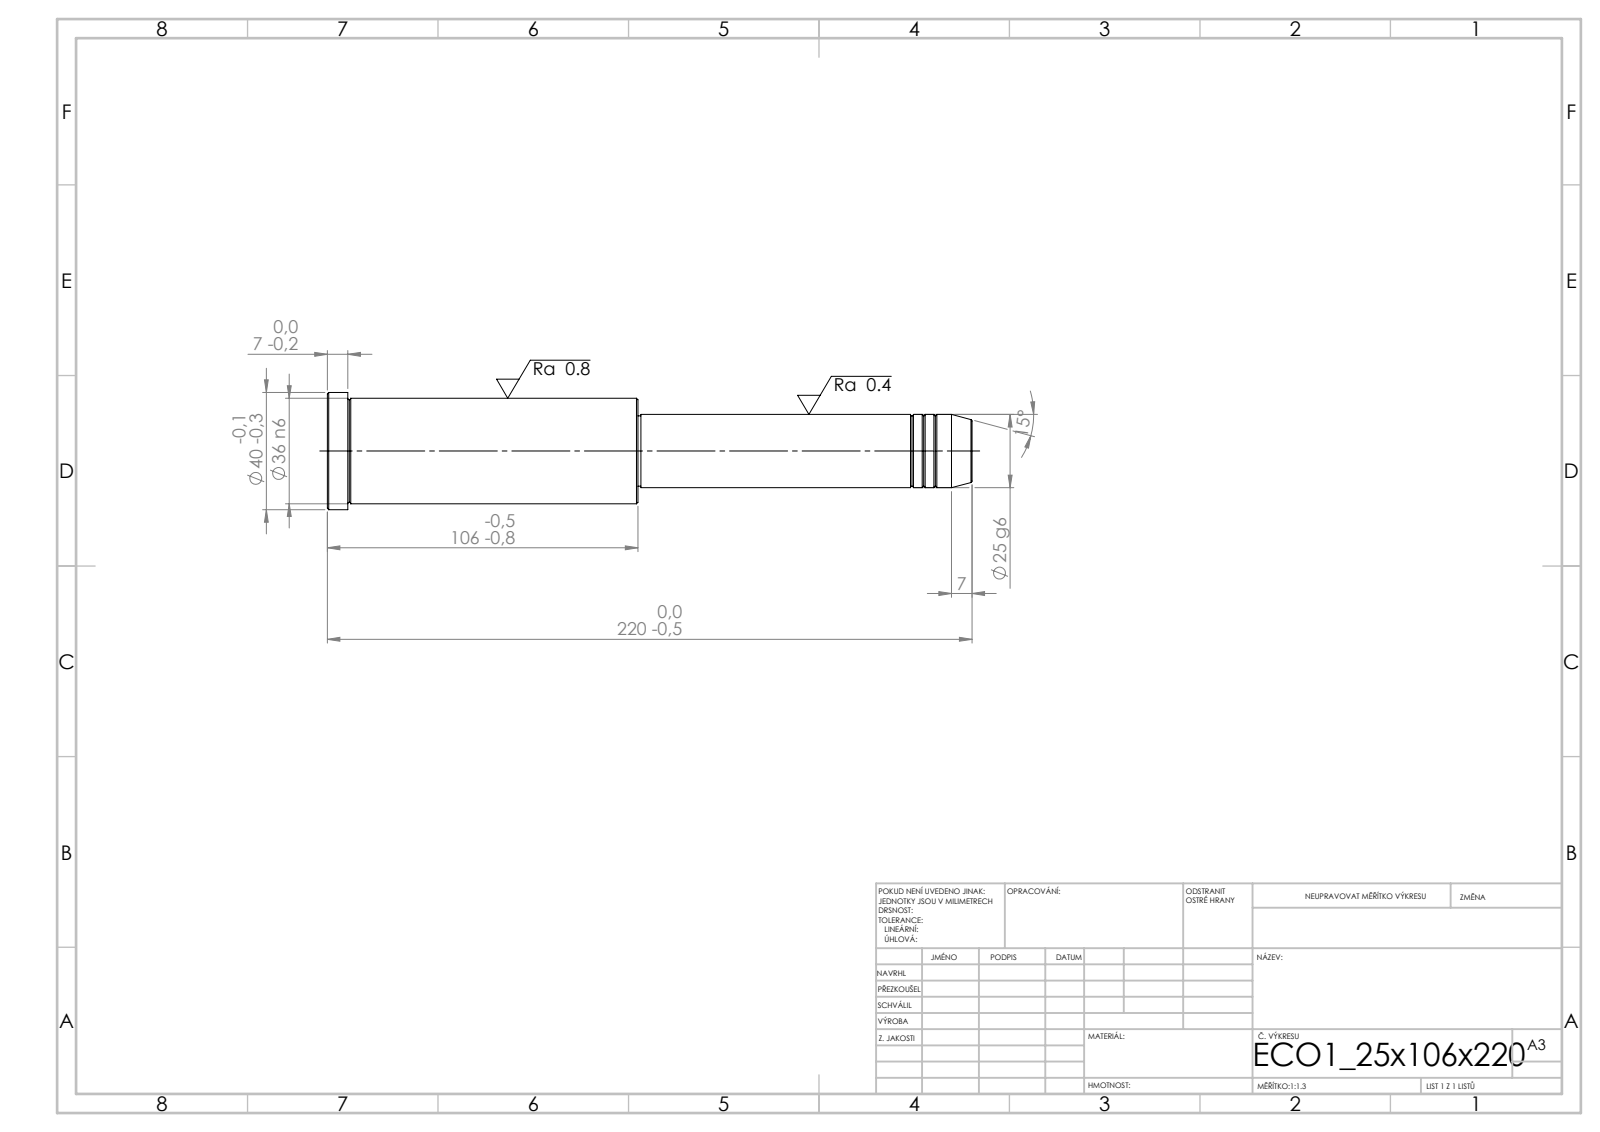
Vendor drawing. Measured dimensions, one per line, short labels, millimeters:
written by: SolidWorks 2019 (CONFIG_CONTROL_DESIGN)
unit: mm
bodies: 1 solid, 43 faces (5 planar, 14 cylindrical, 24 other)
size: 220 × 40 × 40
volume: 164 831 mm³; area: 23 566 mm²
bosses: 1× ⌀40, 1× ⌀36, 1× ⌀25, 1× ⌀24
face distances: 106, 114, 220, 213, 99, 7, 113, 1, 100, 107
